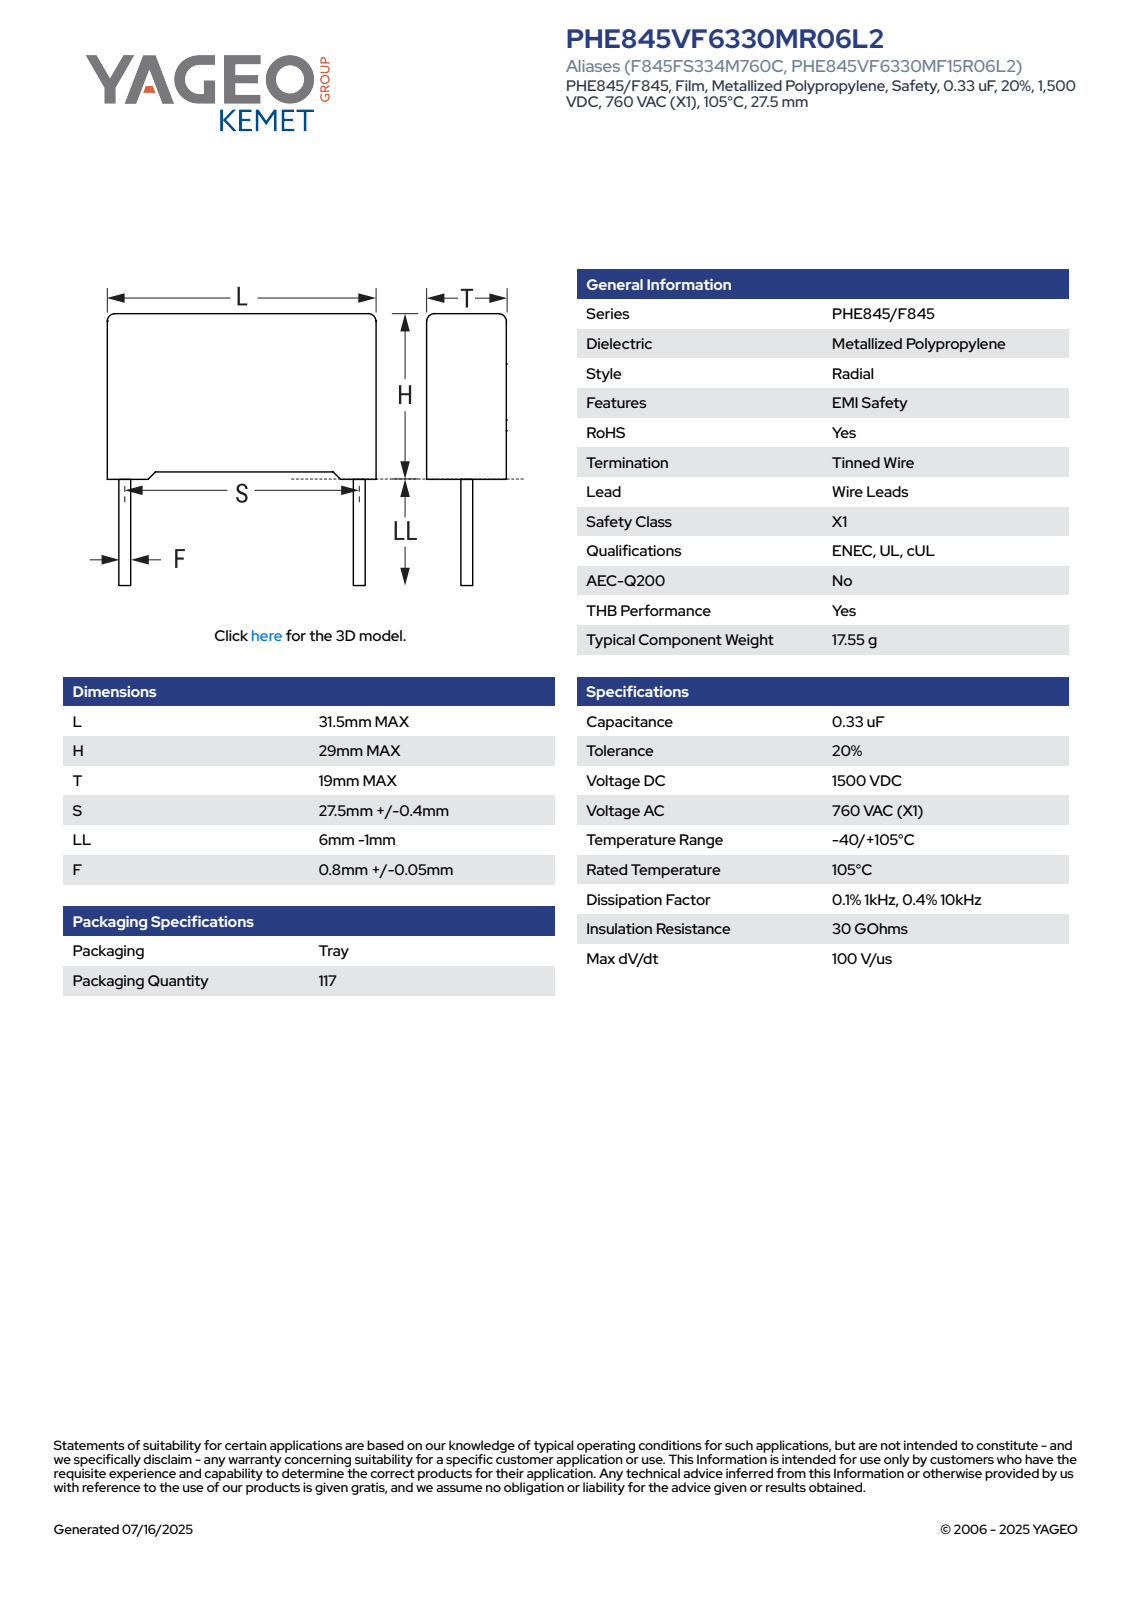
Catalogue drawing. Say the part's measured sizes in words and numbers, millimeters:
The part is named "CFR_RB2_31.5X29X19_L31.5H29T19S27.5LL5F0.8". Its 3-D file was written by "SolidWorks 2021 (AUTOMOTIVE_DESIGN)". It is 4 solids with 85 faces: 77 planar, 8 cylindrical and 0 other. Overall it measures 34 by 31.5 by 19 millimeters. Its volume is 16 838 cubic millimeters and its surface area 4 200 square millimeters. Round bosses or shafts: 2 of diameter 0.8. Partial cylindrical surfaces (rounded edges, fillets, slot ends): 4 of radius 0.5. The main face-to-face distances are 19, 31.5, 28, 28.25, 0.75, 1, 29, 1.05, 30.45, 19.01.
